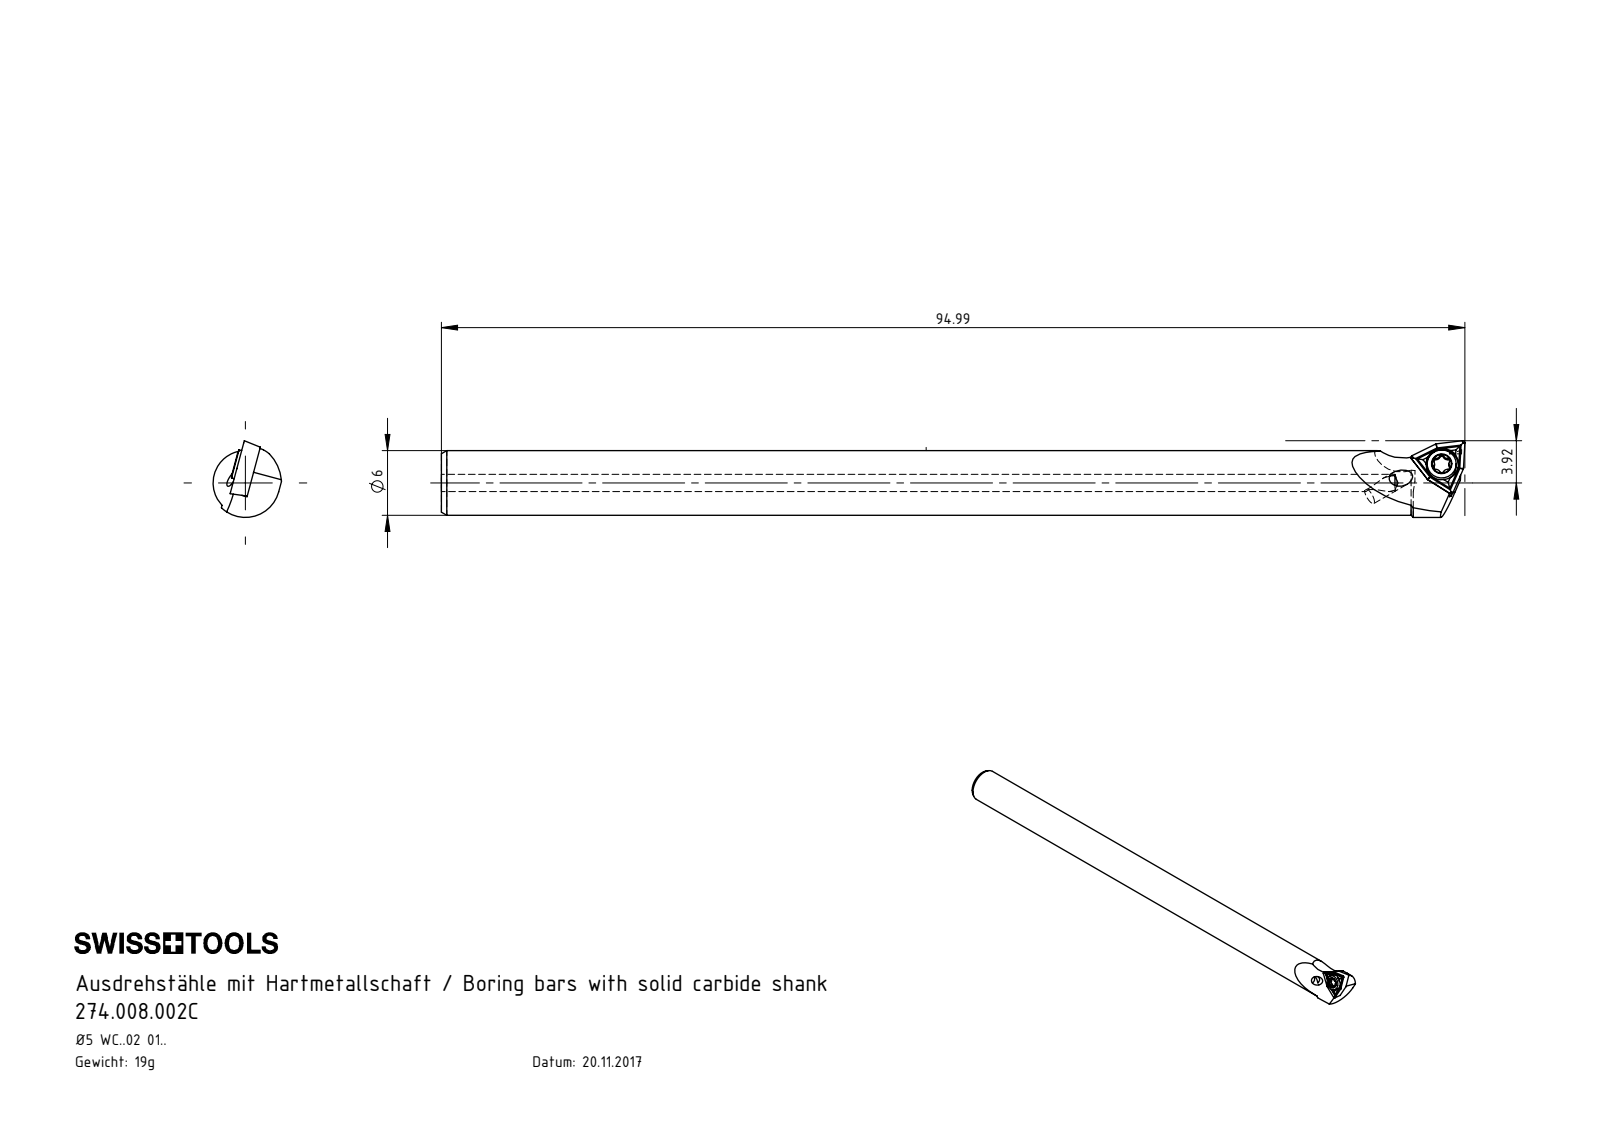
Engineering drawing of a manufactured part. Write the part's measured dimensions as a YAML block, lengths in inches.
part_name: "SFS-Torx-M2; 274.008.002C; B08-WWA.K11.100_A; WCMT020102"
step_written_by: "SolidWorks 2022 (CONFIG_CONTROL_DESIGN)"
units: inches
bodies: {solids: 3, faces: 113, planar: 37, cylindrical: 37, other: 39}
overall_size: [3.74, 0.28, 0.25]
volume: 0.148
surface_area: 3.655
round_holes:
  - {diameter: 0.063, count: 3}
  - {diameter: 0.091, count: 1}
  - {diameter: 0.118, count: 1}
round_bosses_or_shafts:
  - {diameter: 0.236, count: 1}
  - {diameter: 0.106, count: 1}
  - {diameter: 0.079, count: 1}
partial_cylinders:
  - {radius: 0.008, count: 6}
  - {radius: 0.014, count: 6}
  - {radius: 0.138, count: 2}
  - {radius: 0.126, count: 1}
  - {radius: 0.157, count: 1}
  - {radius: 0.394, count: 1}
face_to_face_distances: [0.107, 0.162, 0.055, 0.044, 0.063, 0.118, 0.17, 0.126, 0.063, 0.181]
